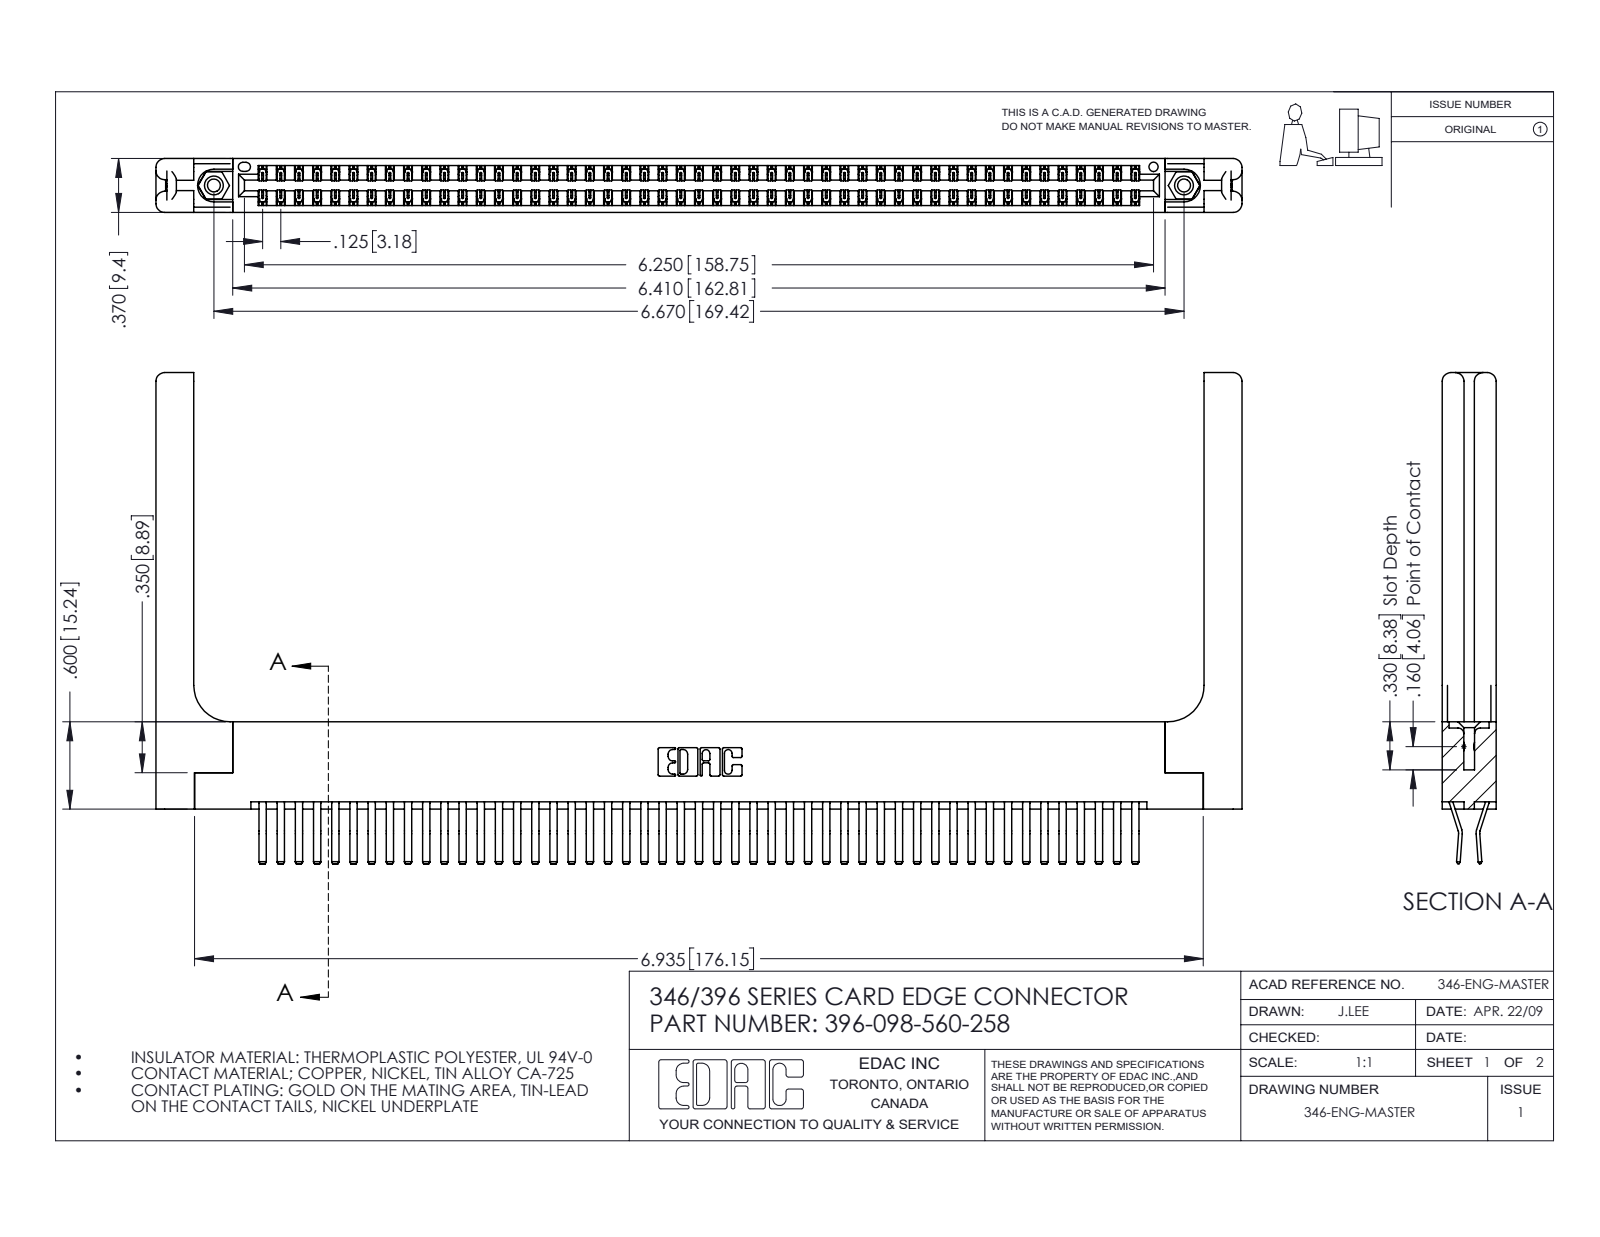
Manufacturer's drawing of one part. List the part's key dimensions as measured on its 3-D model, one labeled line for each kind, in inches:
Part name (STEP PRODUCT): 396-098-560-258; 345-292-001_560 Tail; 346 Part_Flush Mounting Lugs - 0.156 Dia-TH; 346-220-058_345-220-058 (+1 more)
STEP written by: SolidWorks 2016 (CONFIG_CONTROL_DESIGN)
Units: inches
Bodies: 103 solids, 5670 faces (3654 planar, 1956 cylindrical, 60 other)
Overall size (bounding box): 7.466 × 3.375 × 0.37
Volume: 1.628 in³ · Surface area: 51.42 in²
Round holes (diameter × count): ⌀0.089 ×2, ⌀0.125 ×2, ⌀0.156 ×2, ⌀0.064 ×1
Round bosses / shafts (diameter × count): ⌀0.155 ×2
Partial cylindrical surfaces — rounded edges, fillets, slot ends (radius × count): R0.006 ×147, R0.01 ×22, R0.06 ×16, R0.007 ×6, R0.031 ×6, R0.026 ×3, R0.01 ×2, R0.014 ×2
Main face-to-face distances: 0.37, 0.048, 0.322, 0.072, 0.025, 0.148, 0.15, 0.25, 0.298, 0.275
Hole centre spacings: 0.246, 6.461, 6.67
